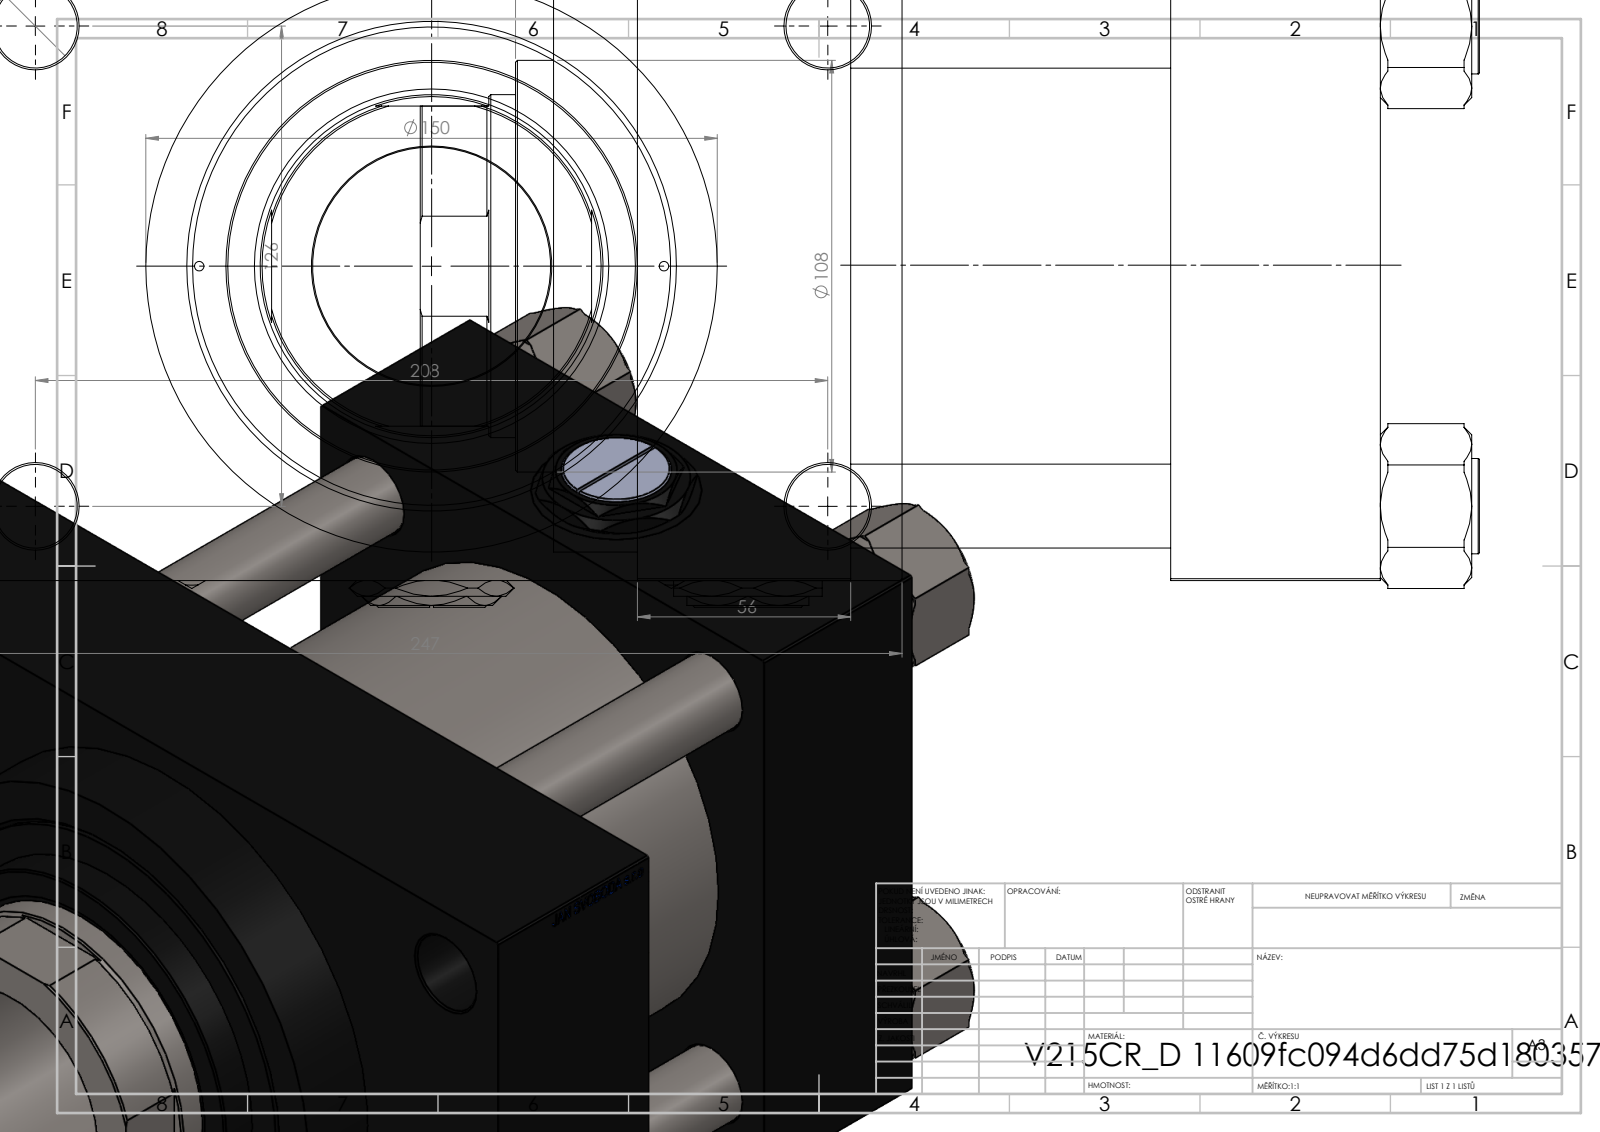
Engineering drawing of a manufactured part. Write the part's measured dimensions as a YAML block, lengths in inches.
part_name: "Zatka_pro_OIL_PORT; V215CR_D_TYCINKA; V215_VC_A; V215CR_D_Body (+2 more)"
step_written_by: "SolidWorks 2019 (CONFIG_CONTROL_DESIGN)"
units: inches
bodies: {solids: 13, faces: 1250, planar: 593, cylindrical: 97, other: 560}
overall_size: [10.945, 9.724, 7.047]
volume: 315.9
surface_area: 905
round_holes:
  - {diameter: 0.866, count: 8}
  - {diameter: 1.269, count: 3}
  - {diameter: 1.772, count: 3}
  - {diameter: 0.098, count: 2}
  - {diameter: 0.276, count: 2}
  - {diameter: 2.461, count: 1}
  - {diameter: 3.543, count: 1}
  - {diameter: 3.661, count: 1}
  - {diameter: 3.78, count: 1}
  - {diameter: 4.921, count: 1}
  - {diameter: 4.941, count: 1}
round_bosses_or_shafts:
  - {diameter: 0.984, count: 4}
  - {diameter: 5.906, count: 1}
  - {diameter: 5.157, count: 1}
  - {diameter: 4.252, count: 1}
partial_cylinders:
  - {radius: 1.732, count: 1}
face_to_face_distances: [6.496, 3.307, 2.165, 5.472, 7.677, 5.512, 2.205, 1.614, 8.11, 6.84]
hole_center_spacings: [1.616, 2.48, 3.003, 3.505, 4.787, 4.957, 5.215, 5.473]
